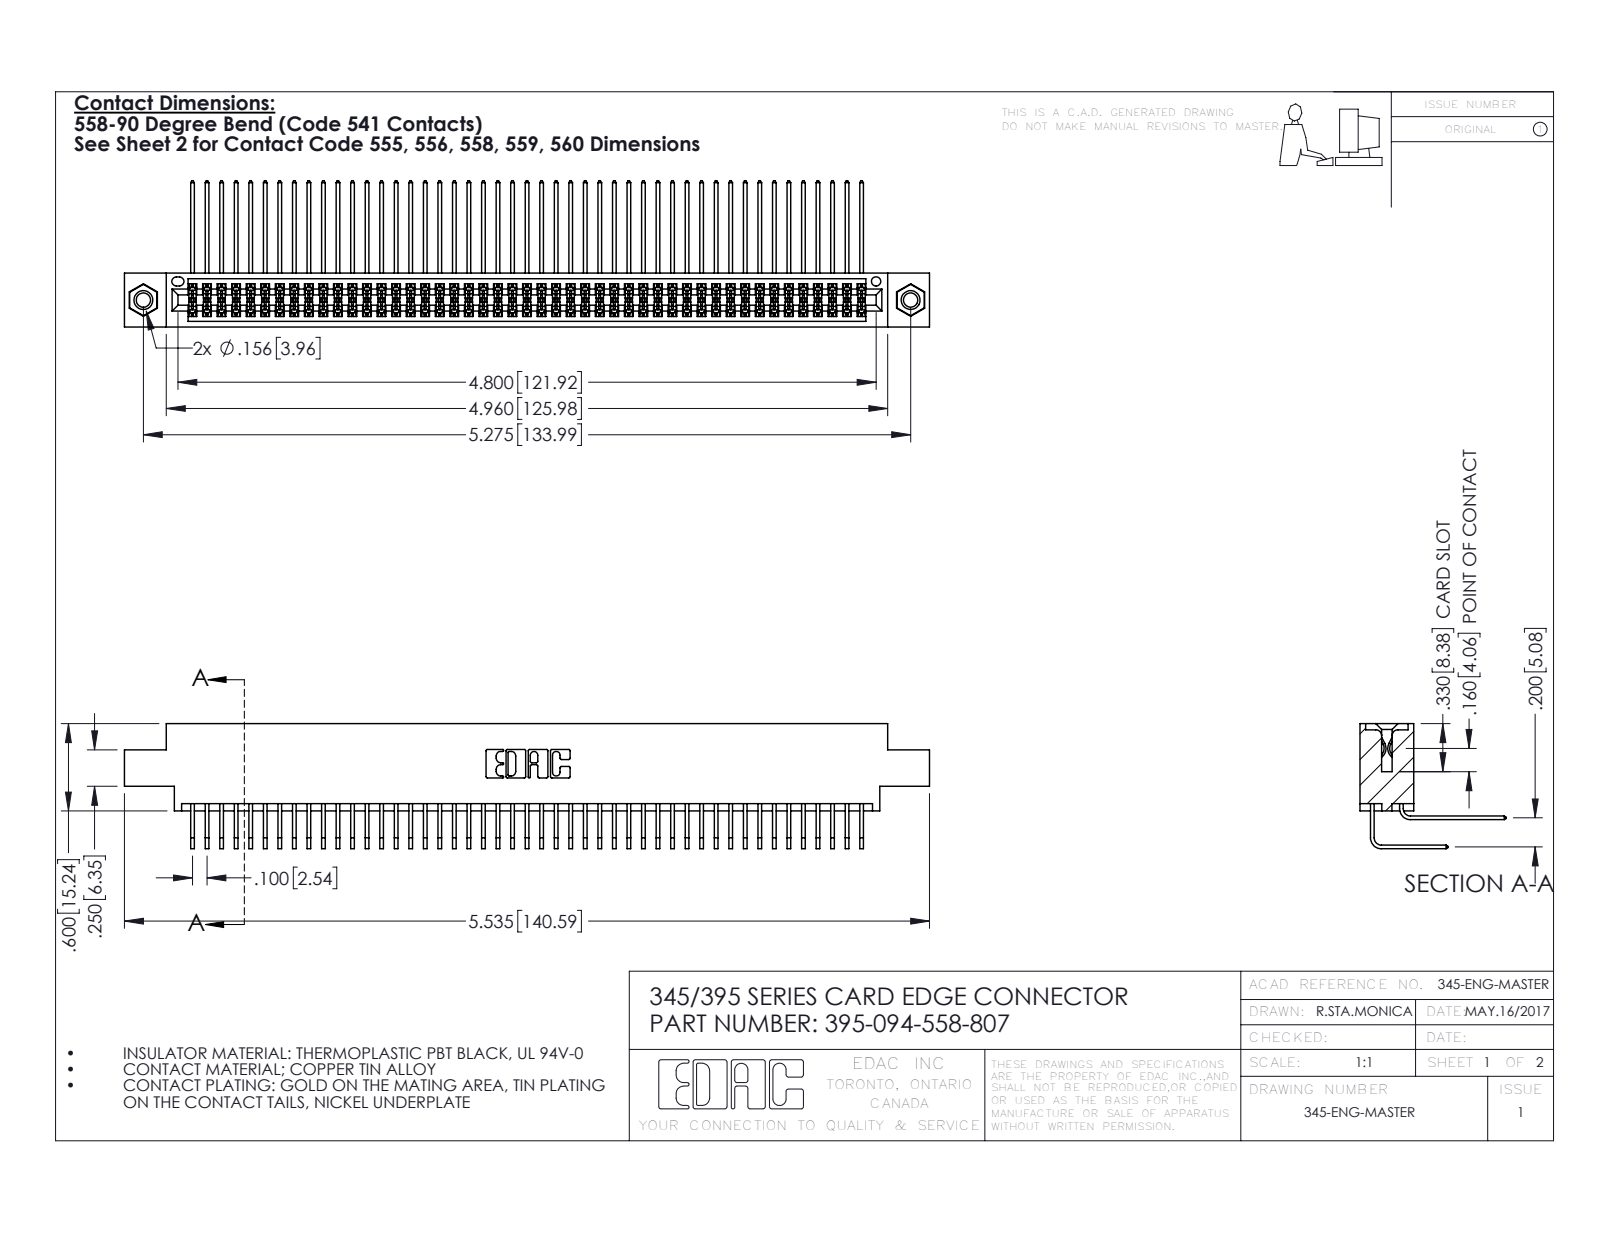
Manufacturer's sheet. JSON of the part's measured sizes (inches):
{"part_name": "345 Part_0.170 Offset - 0.156 Dia-TI; 395-094-558-807; 345-292-001_558 559 Tail - 1; 345-292-001_558 Tail - 2 (+1 more)", "step_written_by": "SolidWorks 2016 (CONFIG_CONTROL_DESIGN)", "units": "inches", "bodies": {"solids": 97, "faces": 5078, "planar": 3406, "cylindrical": 1656, "other": 16}, "overall_size": [5.535, 1.005, 0.859], "volume_in3": 0.862, "surface_area_in2": 36.72, "round_holes": [[0.098, 2], [0.125, 2], [0.156, 2], [0.064, 1]], "round_bosses_or_shafts": [[0.155, 2]], "partial_cylinders_radius": [[0.006, 142], [0.01, 22], [0.007, 6], [0.031, 6], [0.026, 3], [0.014, 2], [0.019, 2], [0.022, 2]], "face_to_face_distances": [0.072, 0.298, 0.2, 0.37, 0.098, 0.272, 0.025, 0.225, 0.175, 0.025], "hole_center_spacings": [0.27, 5.039, 5.275]}
